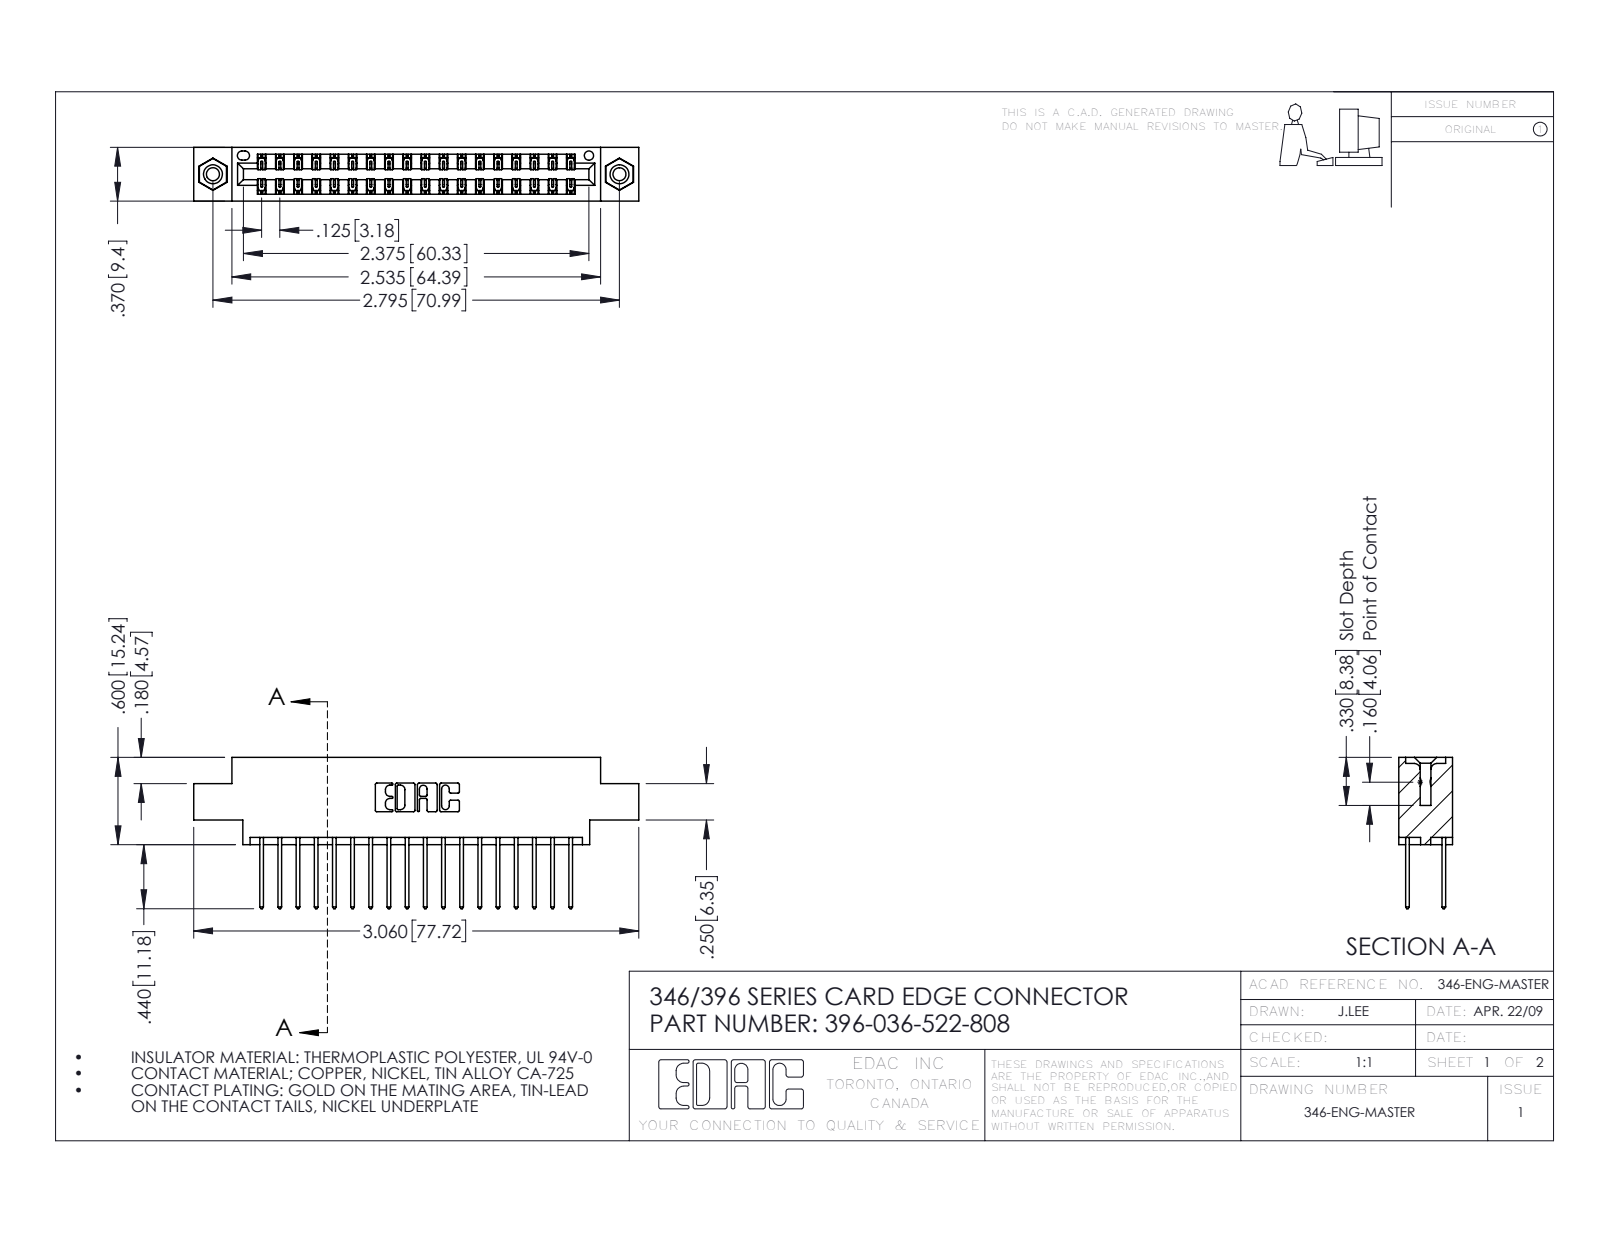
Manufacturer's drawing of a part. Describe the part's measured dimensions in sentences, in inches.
The part is named "345-292-001_345-293-122; 396-036-522-808; 346 Part_0.170 Offset - 0.156 Dia-TI; 345-250-001_345-250-003-102". Its 3-D file was written by "SolidWorks 2016 (CONFIG_CONTROL_DESIGN)". It is 39 solids with 2058 faces: 1372 planar, 670 cylindrical and 16 other. Overall it measures 3.06 by 1.04 by 0.37 inches. Its volume is 0.447 cubic inches and its surface area 15.99 square inches. Round holes: 2 of diameter 0.089, 2 of diameter 0.125, 2 of diameter 0.156, 1 of diameter 0.064. Round bosses or shafts: 2 of diameter 0.155. Partial cylindrical surfaces (rounded edges, fillets, slot ends): 54 of radius 0.006, 36 of radius 0.01, 22 of radius 0.01, 6 of radius 0.007, 6 of radius 0.031, 3 of radius 0.026, 2 of radius 0.014, 2 of radius 0.022. The main face-to-face distances are 0.048, 0.322, 0.25, 0.37, 0.072, 0.298, 0.025, 0.275, 0.222, 0.148. The hole center spacings are 0.246, 2.588, 2.795.
